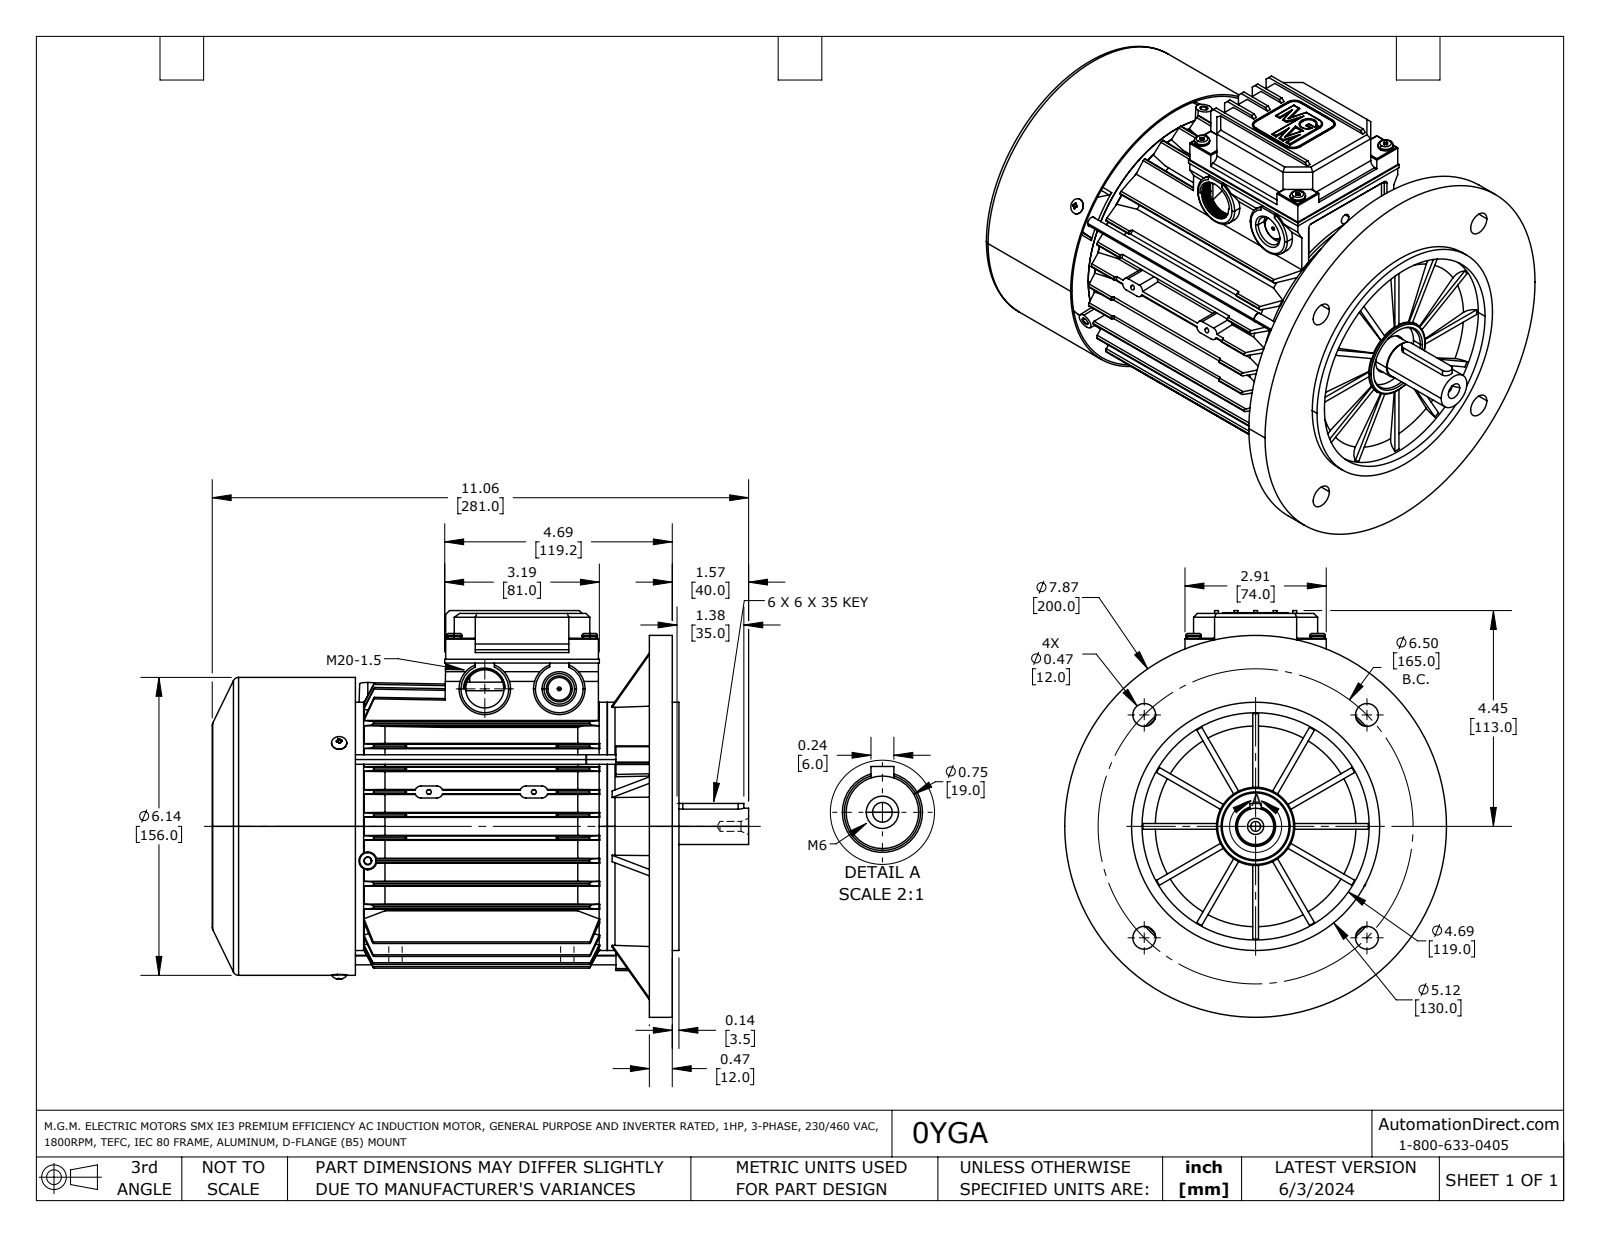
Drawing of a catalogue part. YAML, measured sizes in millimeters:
part_name: "0YGA"
step_written_by: "SolidWorks 2021 (AUTOMOTIVE_DESIGN)"
units: millimeters
bodies: {solids: 21, faces: 2867, planar: 1080, cylindrical: 963, other: 824}
overall_size: [281, 213, 200]
volume: 870300
surface_area: 560400
round_holes:
  - {diameter: 3, count: 12}
  - {diameter: 3.7, count: 8}
  - {diameter: 5.5, count: 8}
  - {diameter: 4, count: 4}
  - {diameter: 12, count: 4}
  - {diameter: 3.2, count: 3}
  - {diameter: 4.2, count: 3}
  - {diameter: 4.5, count: 3}
  - {diameter: 7, count: 3}
  - {diameter: 5.2, count: 1}
  - {diameter: 8, count: 1}
  - {diameter: 16, count: 1}
round_bosses_or_shafts:
  - {diameter: 3, count: 10}
  - {diameter: 8, count: 7}
  - {diameter: 3.5, count: 4}
  - {diameter: 27, count: 3}
  - {diameter: 5, count: 3}
  - {diameter: 2, count: 3}
  - {diameter: 6.3, count: 2}
  - {diameter: 200, count: 1}
partial_cylinders:
  - {radius: 1, count: 266}
  - {radius: 0.4, count: 36}
  - {radius: 0.2, count: 32}
  - {radius: 0.5, count: 30}
  - {radius: 0.9, count: 30}
  - {radius: 0.1, count: 16}
  - {radius: 0.8, count: 16}
  - {radius: 5, count: 9}
face_to_face_distances: [6.5, 2, 83.9, 5.5, 11.8, 72.2, 71.7, 12.2, 59.9, 23.6]
hole_center_spacings: [12.1, 70, 14.5, 19, 28, 31, 31, 39.6]
